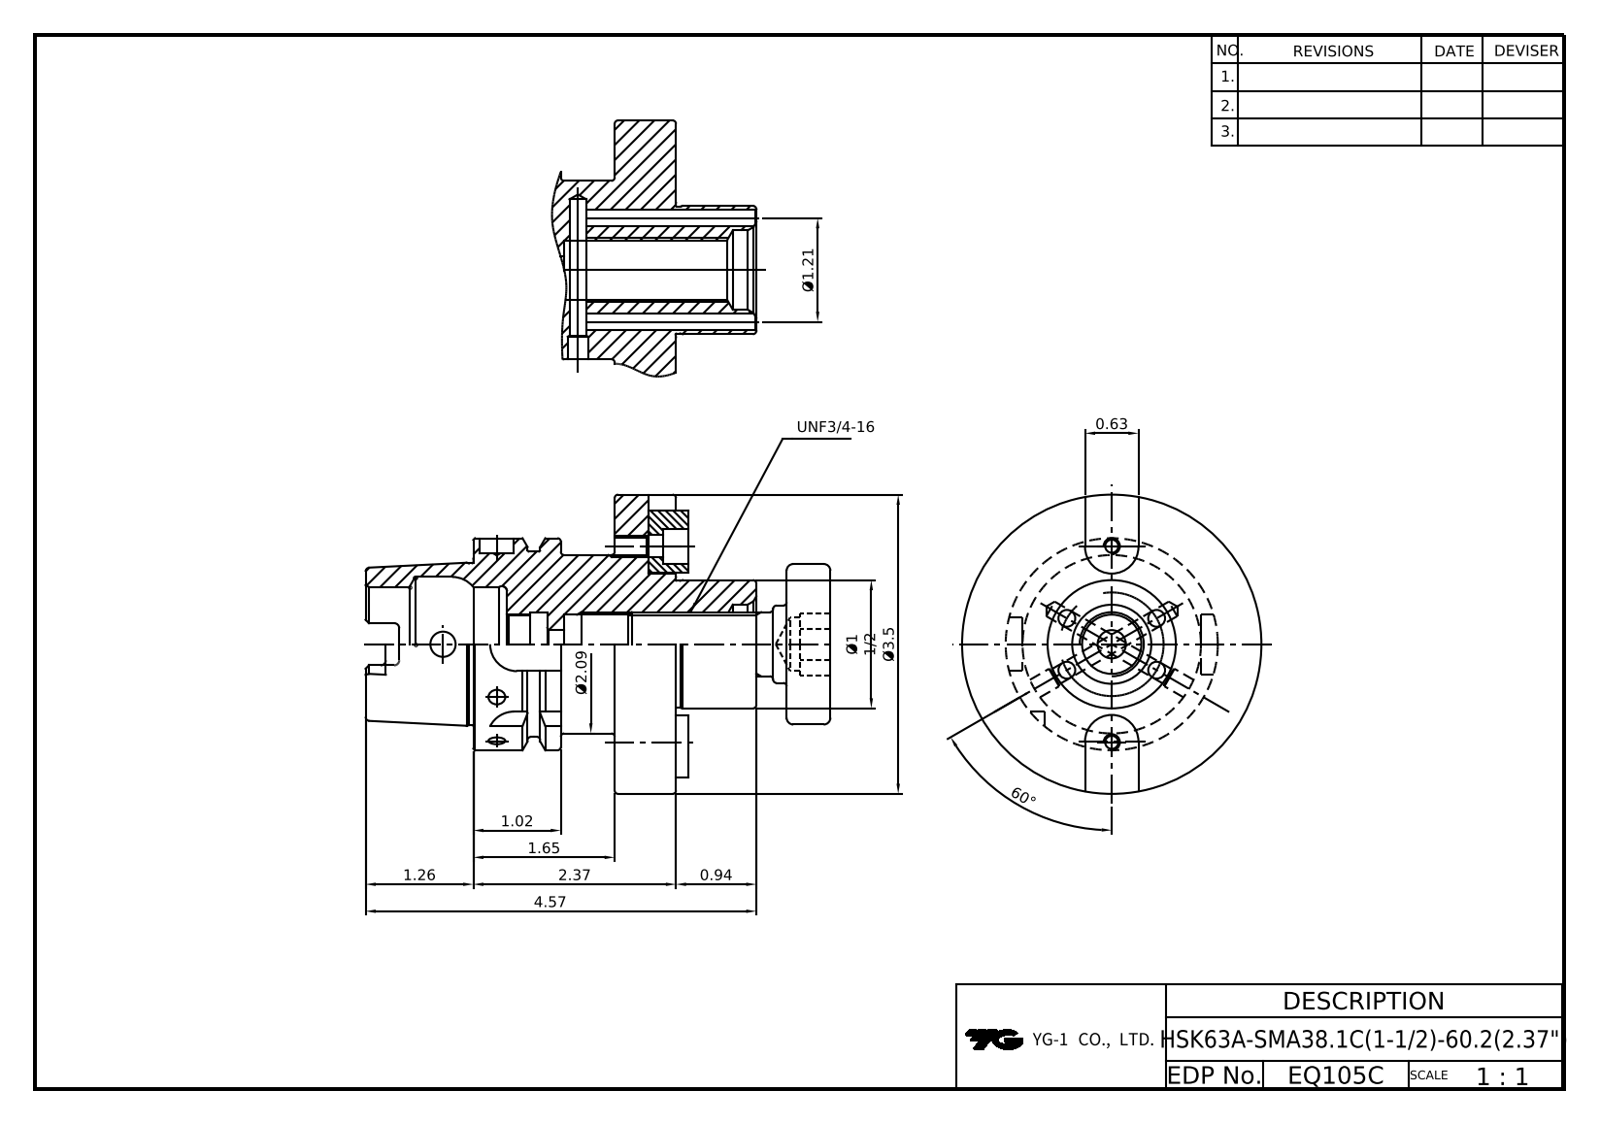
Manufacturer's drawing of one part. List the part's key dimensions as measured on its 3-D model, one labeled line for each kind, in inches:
Part name (STEP PRODUCT): LO-HSK63A-SMA38.1C-60.2; COLLAR BOLT-UNF3_4-16x47L; HEX'' WRENCH BOLT-UNC1_4-20x1_2L; DRIVE KEY-15.875x11.8x18.5
STEP written by: Autodesk Inventor 2025 (AUTOMOTIVE_DESIGN)
Units: inches
Bodies: 6 solids, 225 faces (97 planar, 58 cylindrical, 70 other)
Overall size (bounding box): 5.351 × 3.5 × 3.5
Volume: 16.78 in³ · Surface area: 92.68 in²
Round holes (diameter × count): ⌀0.118 ×4, ⌀0.196 ×2, ⌀0.26 ×2, ⌀0.406 ×2, ⌀0.295 ×1, ⌀0.315 ×1, ⌀0.394 ×1, ⌀0.625 ×1, ⌀0.666 ×1, ⌀0.682 ×1, ⌀0.748 ×1, ⌀0.925 ×1
Round bosses / shafts (diameter × count): ⌀0.375 ×2, ⌀0.25 ×2, ⌀3.5 ×1, ⌀2.48 ×1, ⌀2.165 ×1, ⌀2.087 ×1, ⌀1.891 ×1, ⌀1.878 ×1
Partial cylindrical surfaces — rounded edges, fillets, slot ends (radius × count): R0.059 ×6, R0.113 ×4, R0.312 ×4, R0.315 ×4
Main face-to-face distances: 0.717, 2.438, 1.722, 1.654, 1.926, 1.21, 0.512, 0.399, 0.318, 1.528
Hole centre spacings: 0.606, 0.994, 1.543, 1.05, 1.147, 1.213, 2.294
